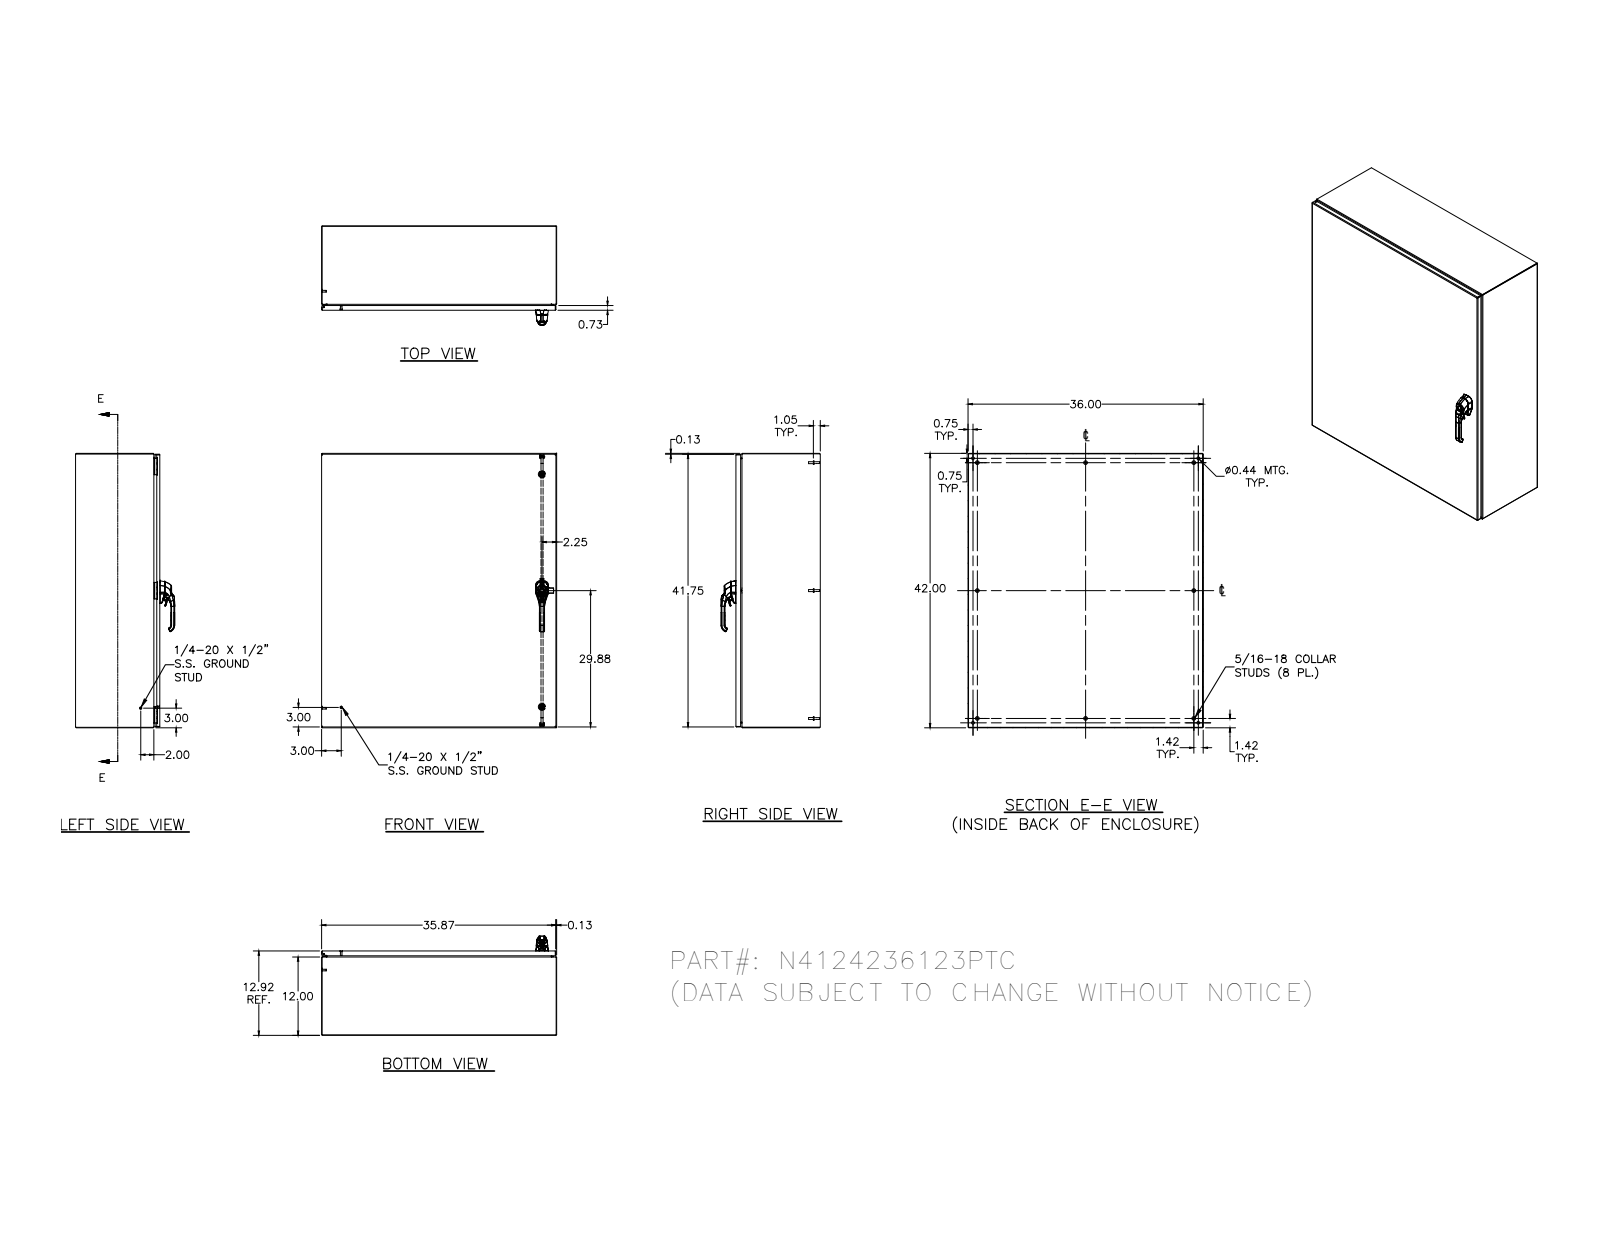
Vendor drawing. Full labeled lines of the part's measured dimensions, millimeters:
Part name (STEP PRODUCT): N4124236123PTC; N4124236123PTCBLR; N41236123PTCTB; HFW328176 (+8 more)
STEP written by: Autodesk Inventor 2011 (AUTOMOTIVE_DESIGN)
Units: millimetres
Bodies: 64 solids, 3420 faces (1104 planar, 1269 cylindrical, 1047 other)
Overall size (bounding box): 1066.8 × 914.4 × 385.7
Volume: 6 379 000 mm³ · Surface area: 6 843 000 mm²
Round holes (diameter × count): ⌀4.8 ×7, ⌀2.4 ×6, ⌀3.9 ×6, ⌀4.2 ×6, ⌀4.4 ×6, ⌀4.2 ×4, ⌀5 ×4, ⌀11.1 ×4, ⌀4 ×3, ⌀5.4 ×3, ⌀6 ×3, ⌀9 ×3
Round bosses / shafts (diameter × count): ⌀6.4 ×14, ⌀14.3 ×8, ⌀7.6 ×8, ⌀7 ×8, ⌀9.1 ×6, ⌀8.1 ×6, ⌀6.5 ×6, ⌀4.2 ×6
Partial cylindrical surfaces — rounded edges, fillets, slot ends (radius × count): R0.5 ×172, R0.3 ×78, R1.3 ×38, R0.8 ×32, R3 ×28, R0.4 ×26, R3.2 ×21, R0.5 ×19
Main face-to-face distances: 1.9, 326.2, 324.3, 328.1, 912.5, 1064.9, 910.6, 914.4, 1063, 1066.8
Hole centre spacings: 482.6, 965.2, 0.4, 16.8, 465.8, 482.4, 482.8, 482.8
